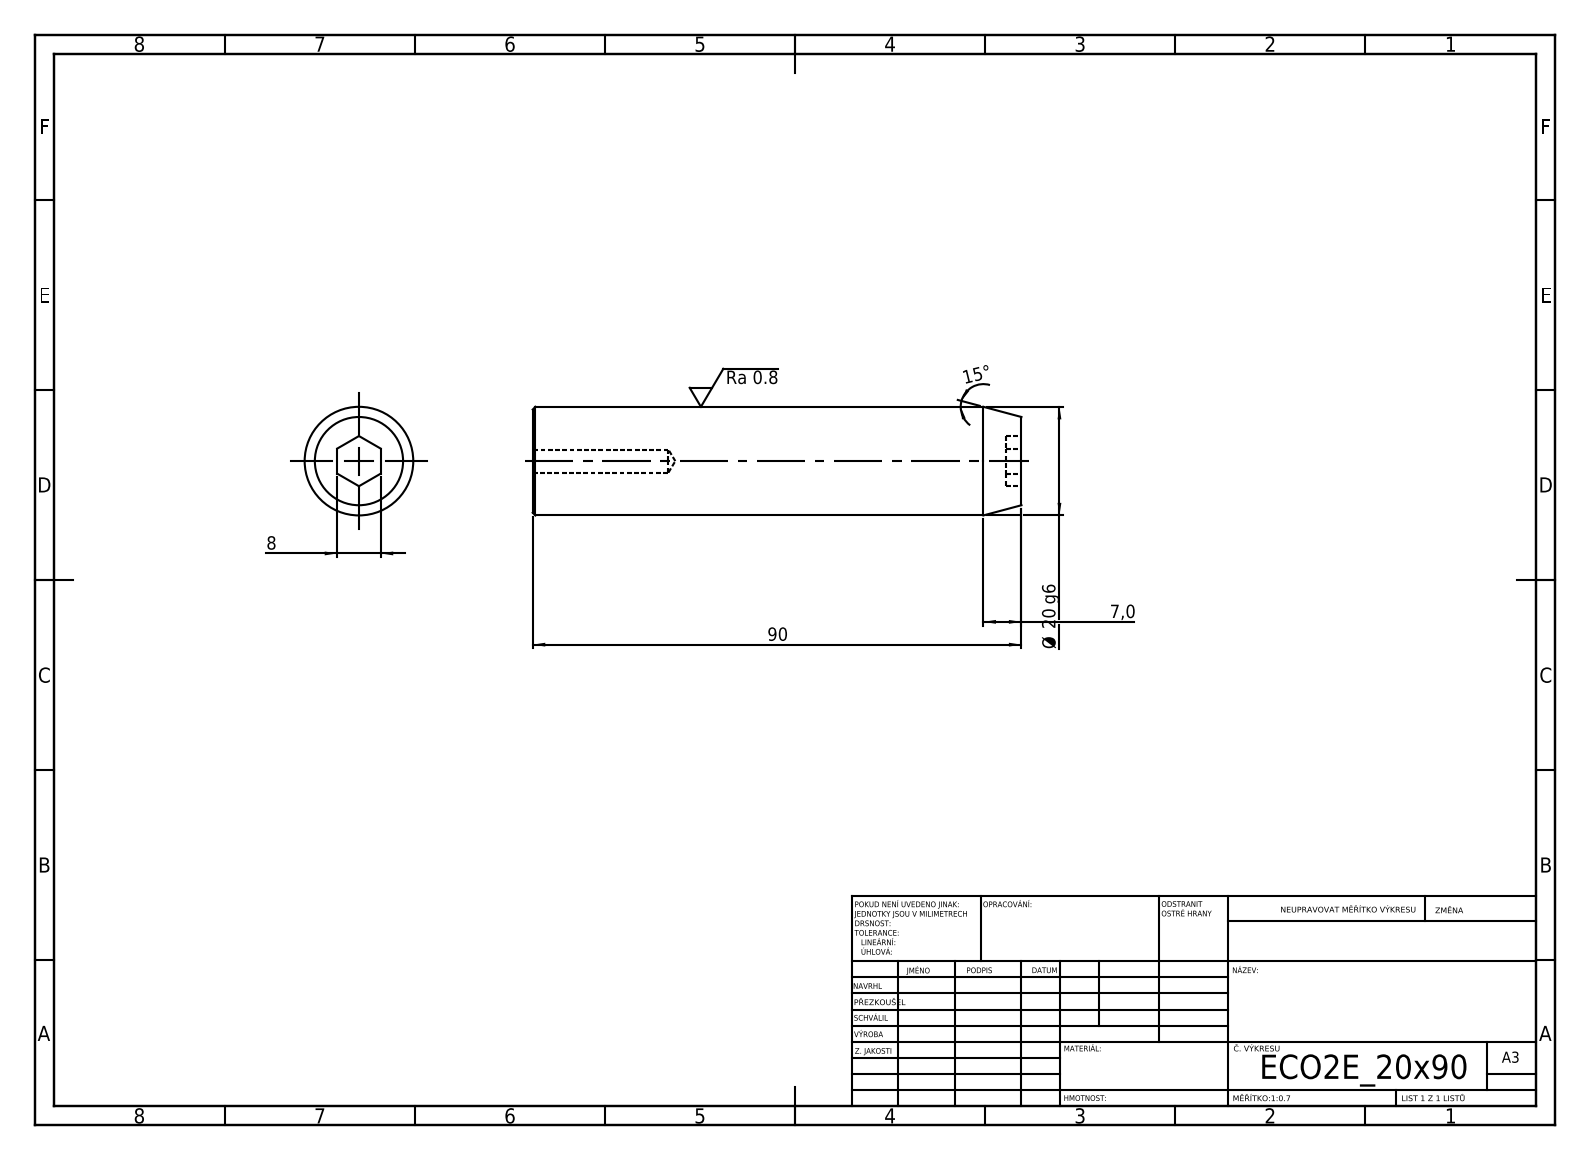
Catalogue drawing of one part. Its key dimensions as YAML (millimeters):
step_written_by: "SolidWorks 2019 (CONFIG_CONTROL_DESIGN)"
units: millimeters
bodies: {solids: 1, faces: 19, planar: 9, cylindrical: 4, other: 6}
overall_size: [90, 20, 20]
volume: 27373
surface_area: 6540
round_holes:
  - {diameter: 4.2, count: 1}
round_bosses_or_shafts:
  - {diameter: 20, count: 1}
face_to_face_distances: [90, 2.8, 87.2, 8]
